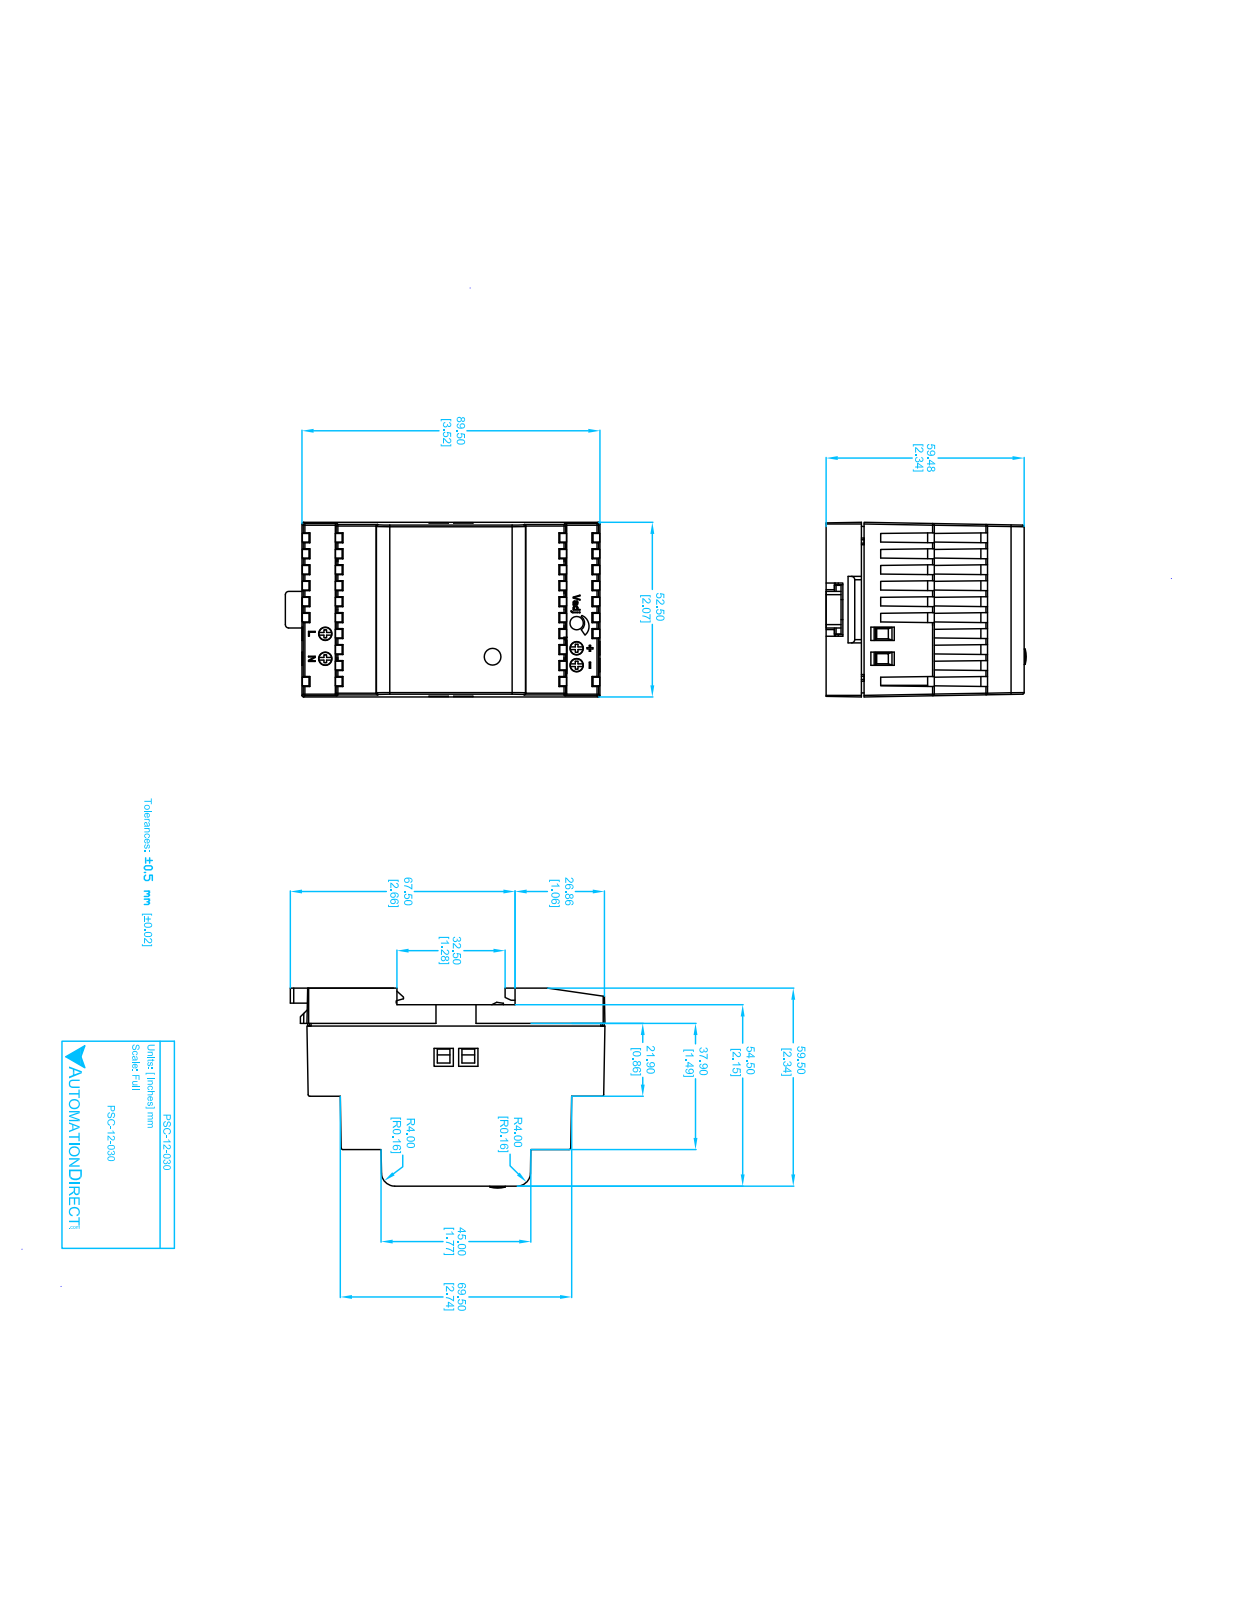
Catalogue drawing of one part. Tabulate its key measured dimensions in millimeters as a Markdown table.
| quantity | value |
| --- | --- |
| part name | PSC-12-030 SLDPRT |
| STEP written by | SolidWorks 2011 (CONFIG_CONTROL_DESIGN) |
| units | millimeters |
| bodies | 1 solid, 605 faces (488 planar, 81 cylindrical, 36 other) |
| overall size | 94.5 × 60.2 × 52.6 |
| volume | 208 800 mm³ |
| surface area | 33 410 mm² |
| round holes (diameter × count) | 4.1 × 5 |
| round bosses / shafts (diameter × count) | 5.1 × 1 |
| partial cylindrical surfaces (radius × count) | 0.5 × 26, 1 × 2, 4.1 × 2 |
| main face-to-face distances | 4.8, 4.8, 9.6, 15.1, 52.6, 10.6, 4.5, 48.3, 59.5, 54.6 |
| hole center spacings | 5.1, 6.4, 7.6, 11.4, 76.7, 76.7, 76.8, 76.8 |
